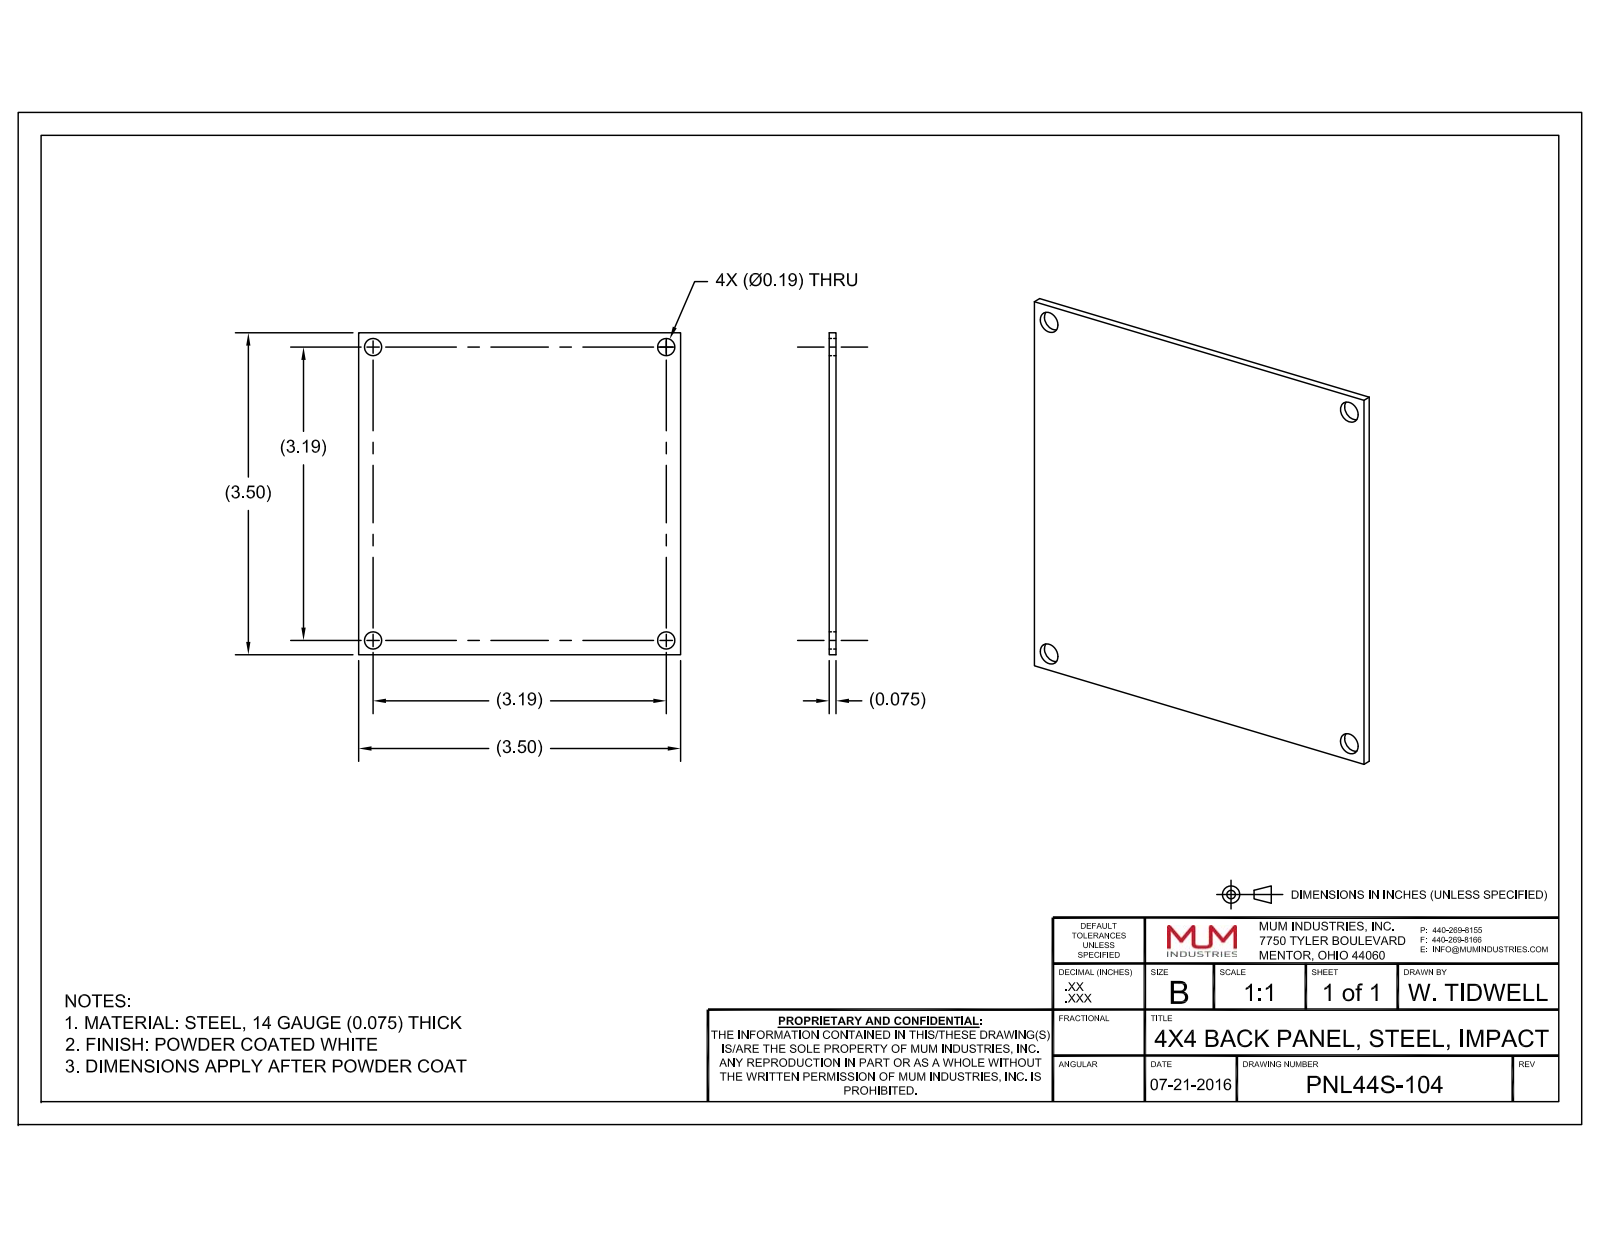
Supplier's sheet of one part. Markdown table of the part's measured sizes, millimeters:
| quantity | value |
| --- | --- |
| part name | PNL44S-104; 9912597-82-10; SBP44-IMP_ASM |
| STEP written by | CREO PARAMETRIC BY PTC INC, 2016050 (CONFIG_CONTROL_DESIGN) |
| units | millimeters |
| bodies | 5 solids, 422 faces (110 planar, 152 cylindrical, 160 other) |
| overall size | 89.1 × 89.1 × 12.4 |
| volume | 15 700 mm³ |
| surface area | 17 770 mm² |
| round holes (diameter × count) | 4.7 × 4 |
| round bosses / shafts (diameter × count) | 8.2 × 4, 4.2 × 4, 3 × 4 |
| main face-to-face distances | 1.9, 88.9, 4.8, 2.9, 3.1, 1.2, 1.7, 79.8, 7.6, 9.5 |
| hole center spacings | 80.9, 114.5 |
